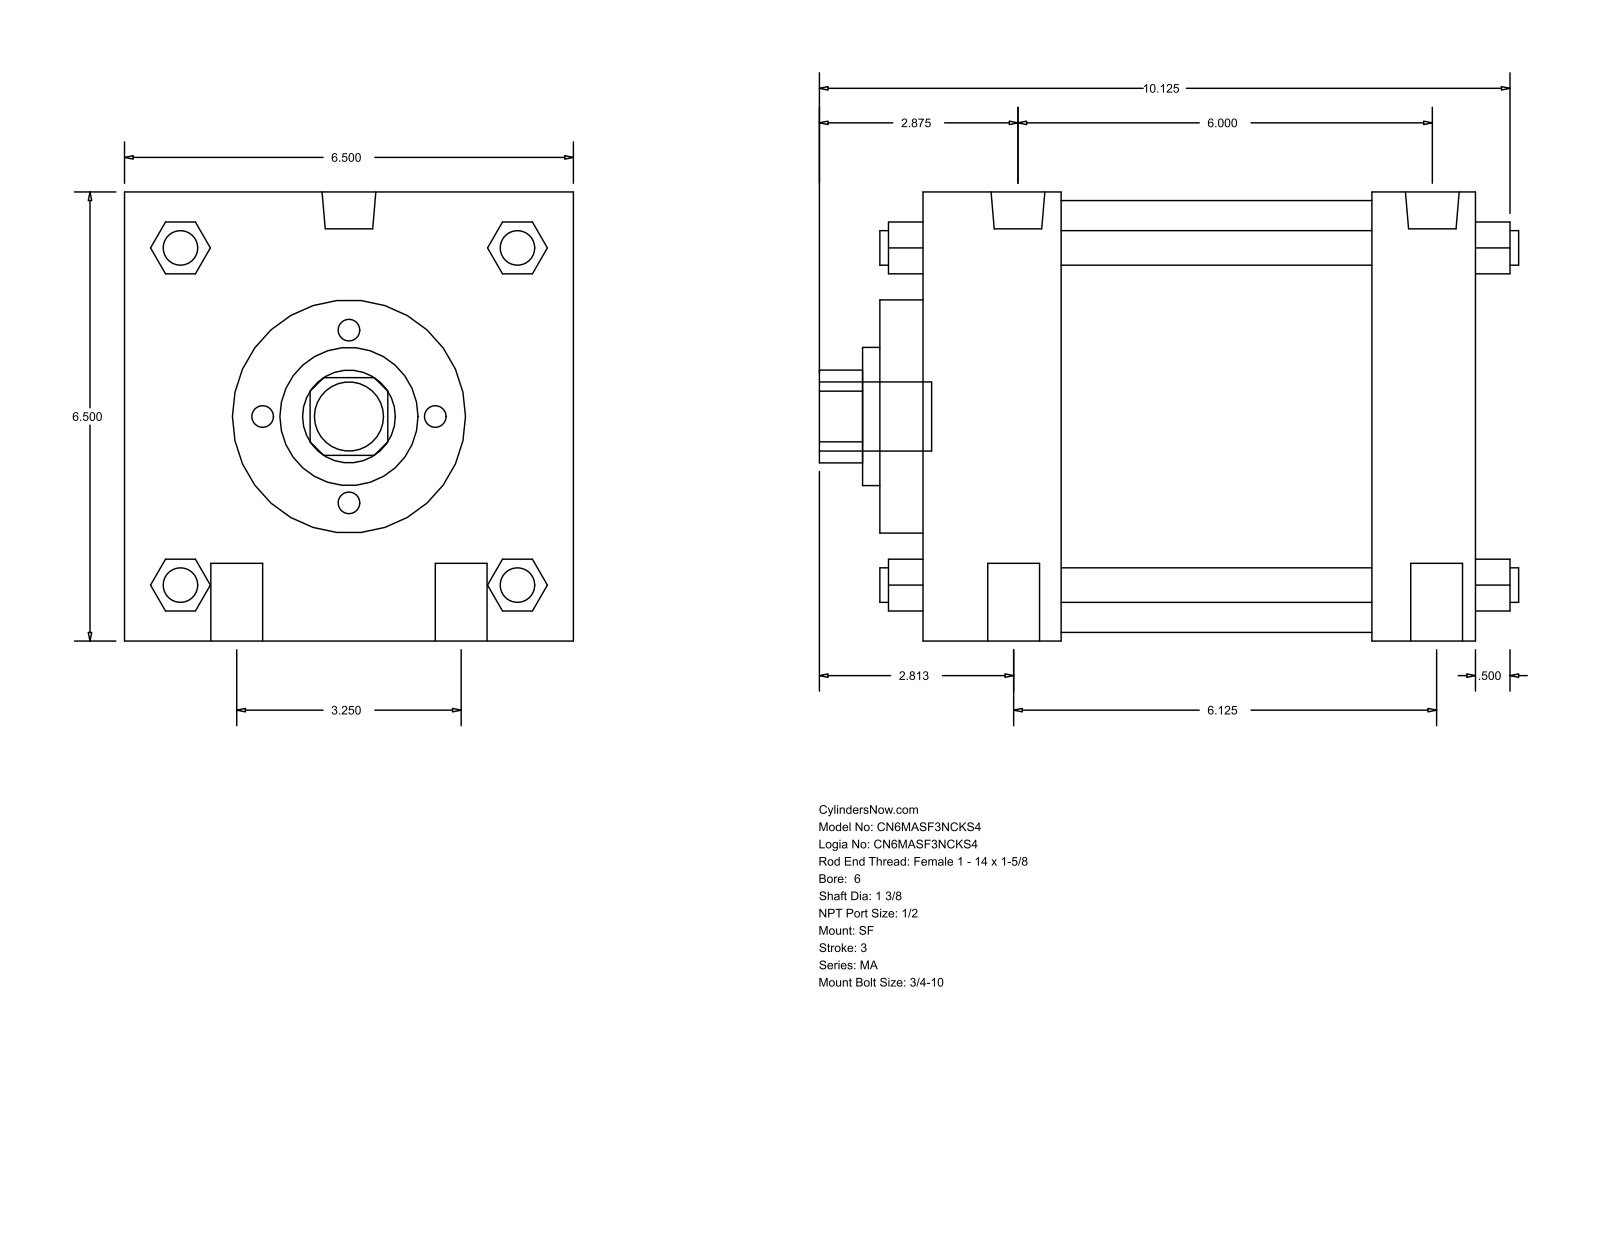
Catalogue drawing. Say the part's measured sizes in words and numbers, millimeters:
The part is named "MA_SF__0600_1.375". Its 3-D file was written by "GSSL Pune (CONFIG_CONTROL_DESIGN)". It is 0 solids with 126 faces: 95 planar, 31 cylindrical and 0 other. Overall it measures 257.18 by 165.1 by 165.1 millimeters. Round holes: 1 of diameter 34.92, 1 of diameter 50.8, 1 of diameter 85.72, 1 of diameter 158.75. Round bosses or shafts: 4 of diameter 19.05, 4 of diameter 12.7, 2 of diameter 19.77, 2 of diameter 17.46, 1 of diameter 25.4. Partial cylindrical surfaces (rounded edges, fillets, slot ends): 1 of radius 17.06. The main face-to-face distances are 165.1, 203.2, 152.4, 50.8, 38.1, 114.3, 15.87, 66.67, 180.97, 219.07.
